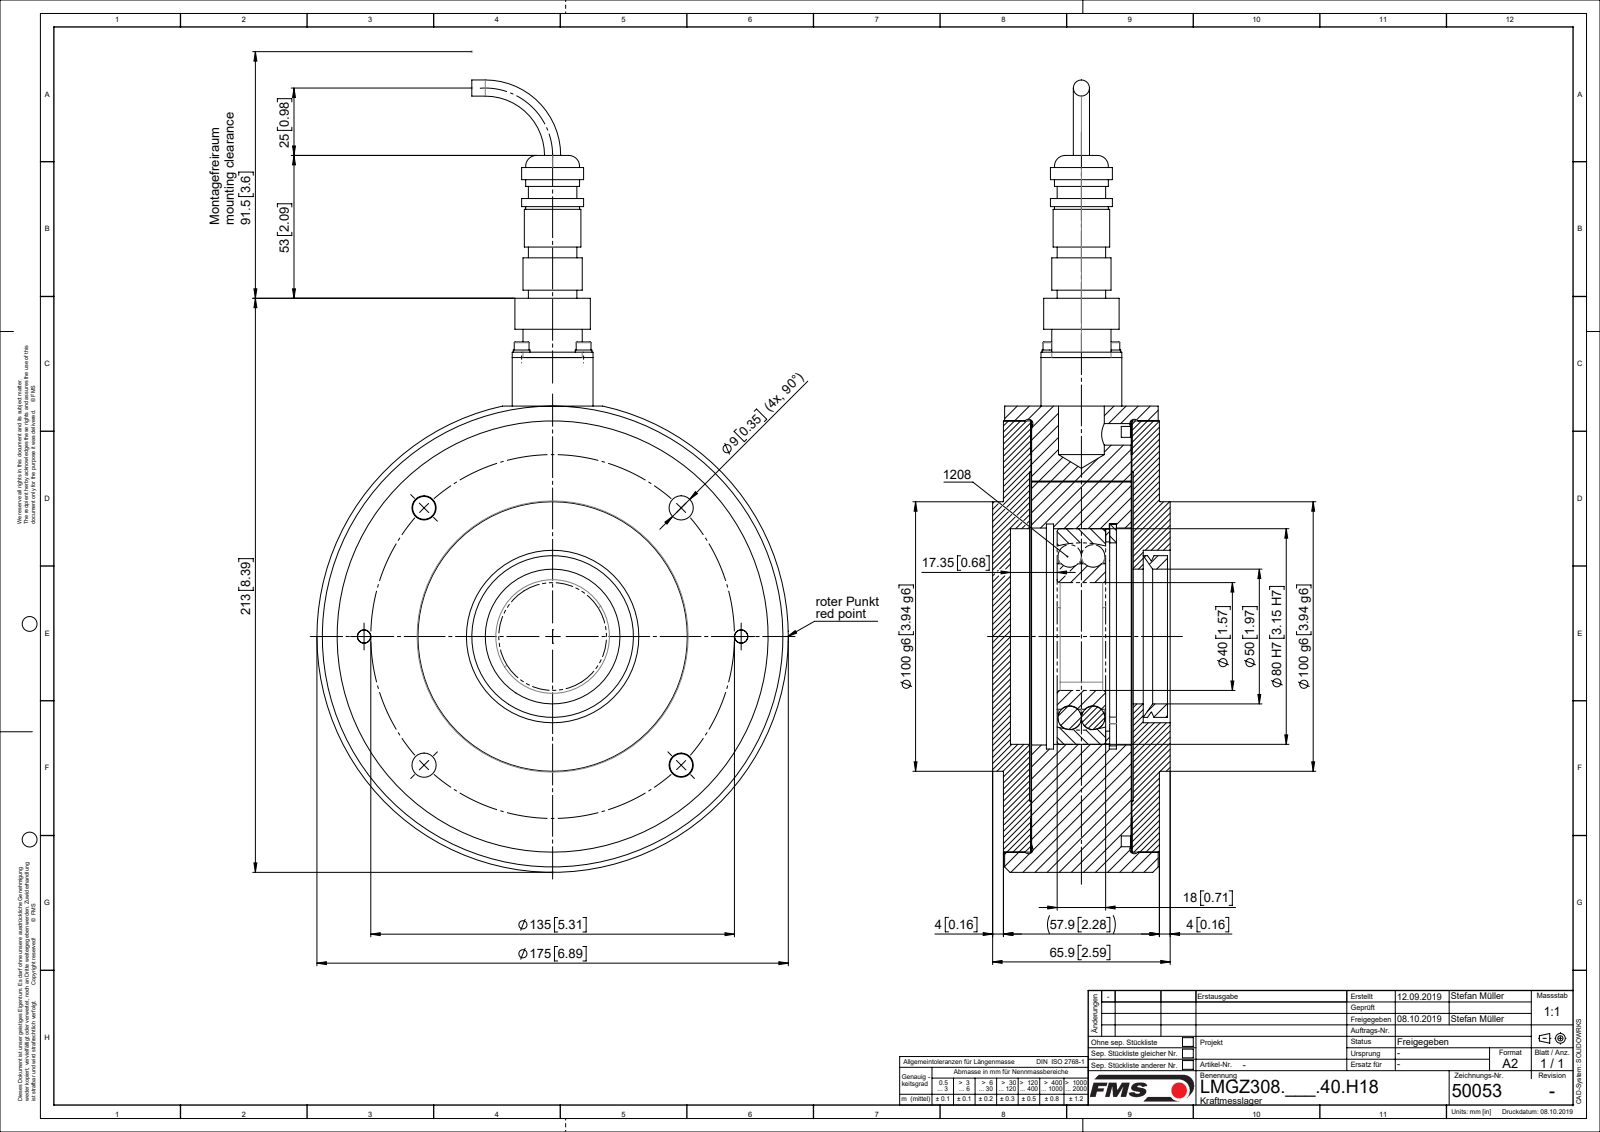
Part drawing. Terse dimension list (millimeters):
name: L50053; L4857104; TEIL1; L49015 (+8 more)
written by: Mechanical Desktop 2007 (CONFIG_CONTROL_DESIGN)
unit: mm
bodies: 22 solids, 380 faces (91 planar, 235 cylindrical, 54 other)
size: 294 × 175 × 65.9
volume: 1 276 000 mm³; area: 275 583 mm²
holes: 4× ⌀2.6, 4× ⌀3.2, 4× ⌀3.4, 4× ⌀9, 2× ⌀5.15, 2× ⌀6.6, 2× ⌀8.68, 2× ⌀11, 1× ⌀40, 1× ⌀48, 1× ⌀50, 1× ⌀62.1
bosses: 4× ⌀6.2, 4× ⌀5.5, 4× ⌀3, 4× ⌀2.5, 3× ⌀6, 2× ⌀10, 1× ⌀175, 1× ⌀160
rounds: 4× R4, 2× R7.5
face distances: 37.25, 10.2, 10.45, 47.45, 47.7, 37, 37.5, 38, 9.75, 9.7
hole spacings: 23, 52.67, 67.5, 95.46, 127.04, 32.53, 70, 135
